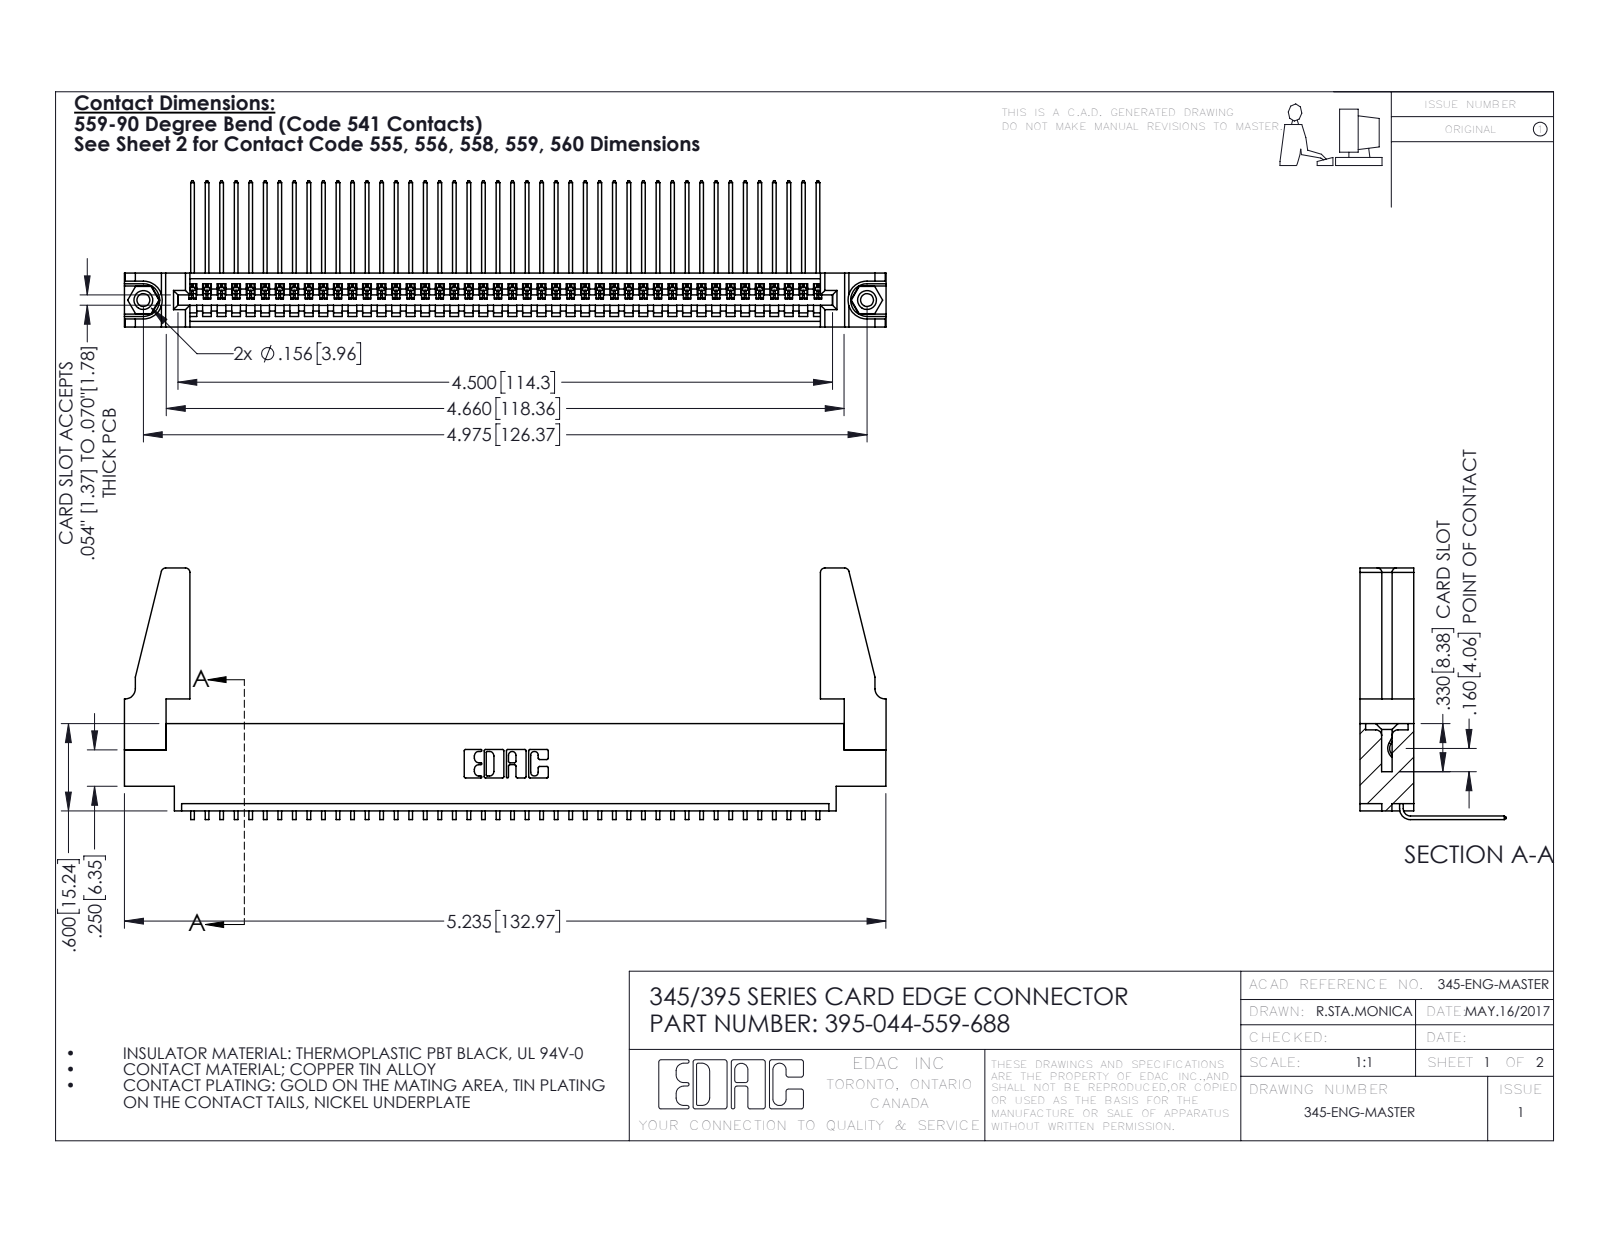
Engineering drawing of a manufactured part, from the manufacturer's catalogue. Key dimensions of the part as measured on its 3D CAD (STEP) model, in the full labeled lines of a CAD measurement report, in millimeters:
Part name (STEP PRODUCT): 345-250-001_345-250-001-102; 345-292-001_558 559 Tail - 1; 345-220-078_345-220-088; 395-044-559-688 (+1 more)
STEP written by: SolidWorks 2016 (CONFIG_CONTROL_DESIGN)
Units: millimetres
Bodies: 49 solids, 2894 faces (2004 planar, 874 cylindrical, 16 other)
Overall size (bounding box): 133 × 43.9 × 25.5
Volume: 15 900 mm³ · Surface area: 21 000 mm²
Round holes (diameter × count): ⌀2.3 ×2, ⌀3.2 ×2, ⌀4 ×2, ⌀1.6 ×1
Round bosses / shafts (diameter × count): ⌀3.9 ×2
Partial cylindrical surfaces — rounded edges, fillets, slot ends (radius × count): R0.2 ×88, R0.3 ×22, R0.8 ×8, R0.2 ×6, R0.8 ×6, R0.7 ×3, R0.8 ×2, R1 ×2
Main face-to-face distances: 9.4, 1.8, 7.6, 5.1, 2.5, 6.9, 0.6, 5.7, 4.4, 3.8
Hole centre spacings: 6.9, 120.4, 126.4
